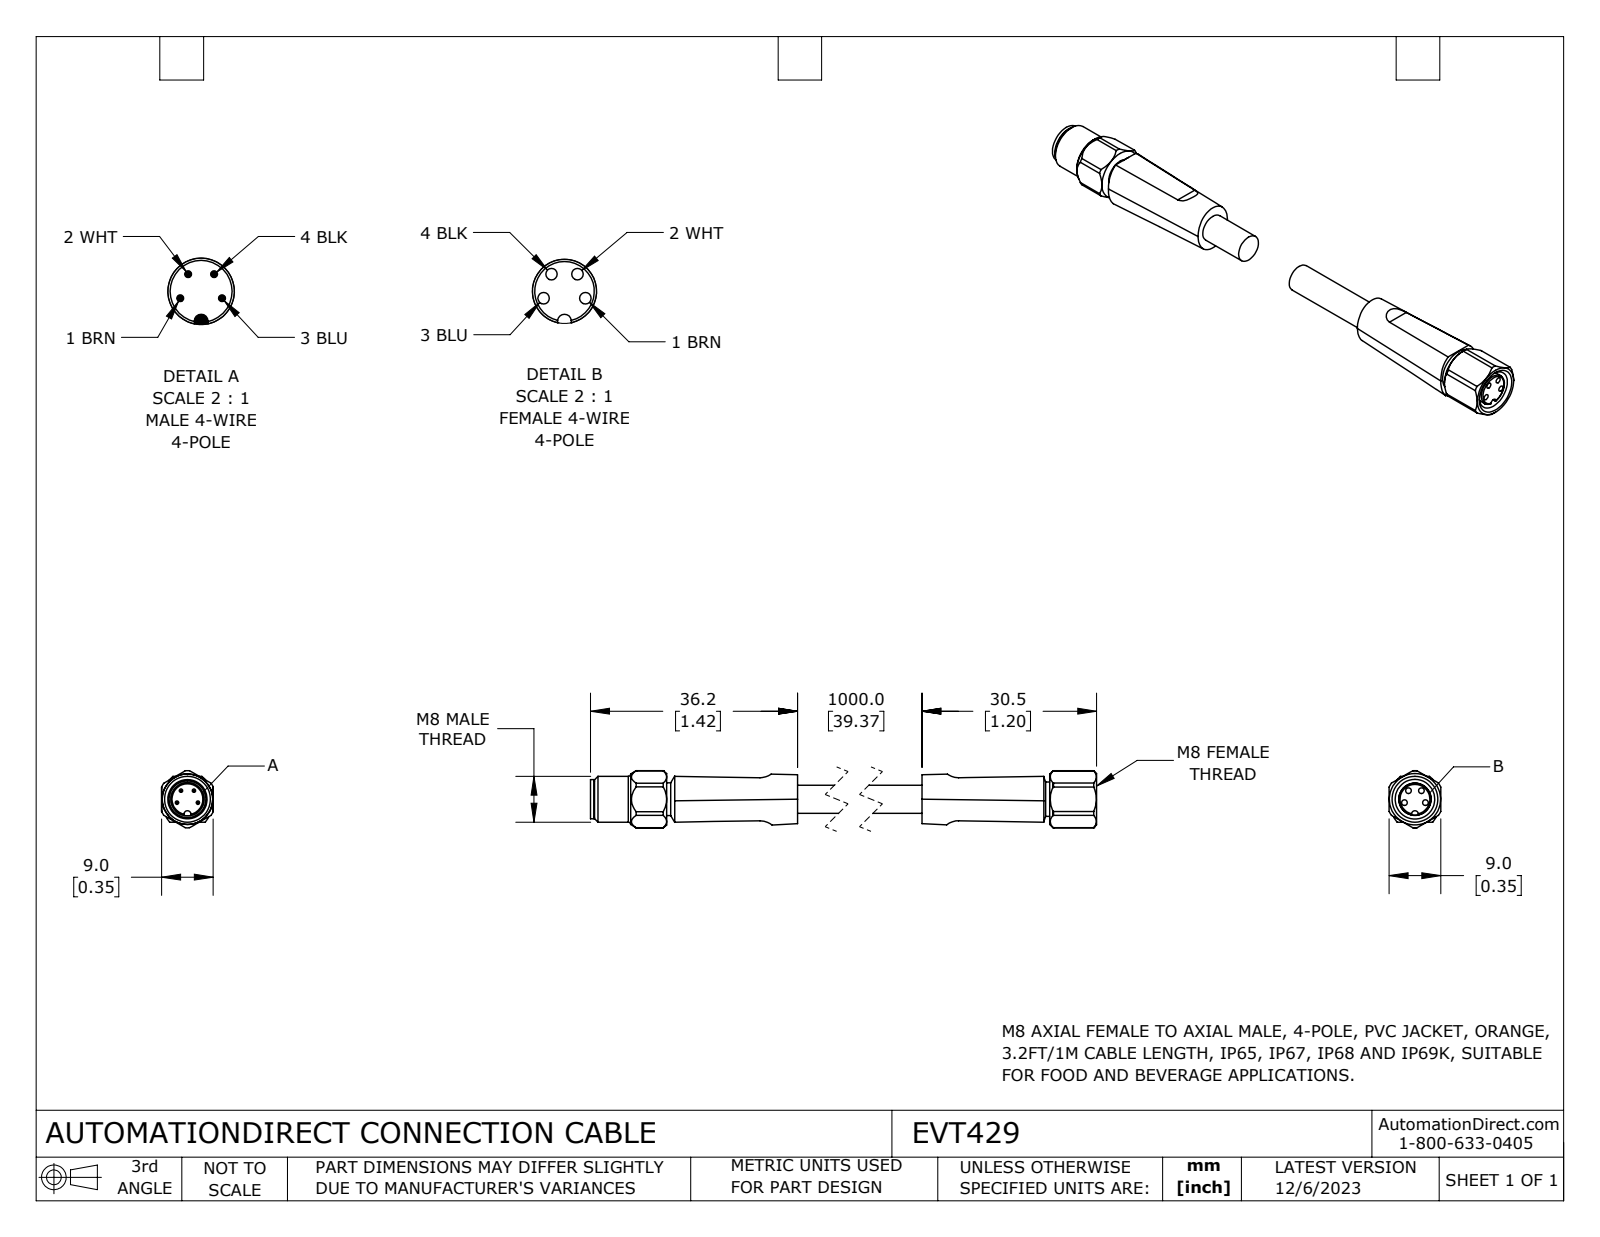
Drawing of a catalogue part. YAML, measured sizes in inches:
part_name: "EVT429_FEMALE; EVT429; EVT429_MALE"
step_written_by: "SolidWorks 2023 (CONFIG_CONTROL_DESIGN)"
units: inches
bodies: {solids: 2, faces: 150, planar: 47, cylindrical: 58, other: 45}
overall_size: [4.173, 0.393, 0.354]
volume: 0.244
surface_area: 4.751
round_holes:
  - {diameter: 0.039, count: 4}
  - {diameter: 0.228, count: 1}
  - {diameter: 0.272, count: 1}
round_bosses_or_shafts:
  - {diameter: 0.023, count: 4}
  - {diameter: 0.315, count: 1}
  - {diameter: 0.27, count: 1}
  - {diameter: 0.248, count: 1}
  - {diameter: 0.236, count: 1}
  - {diameter: 0.224, count: 1}
  - {diameter: 0.222, count: 1}
  - {diameter: 0.193, count: 1}
partial_cylinders:
  - {radius: 0.133, count: 4}
  - {radius: 0.024, count: 1}
  - {radius: 0.196, count: 1}
  - {radius: 0.196, count: 1}
face_to_face_distances: [0.354, 0.26, 0.26, 0.354, 3.327, 1.201, 2.449, 0.878, 0.9, 1.549]
hole_center_spacings: [0.074, 0.076, 0.087, 0.143, 0.089, 0.143]
